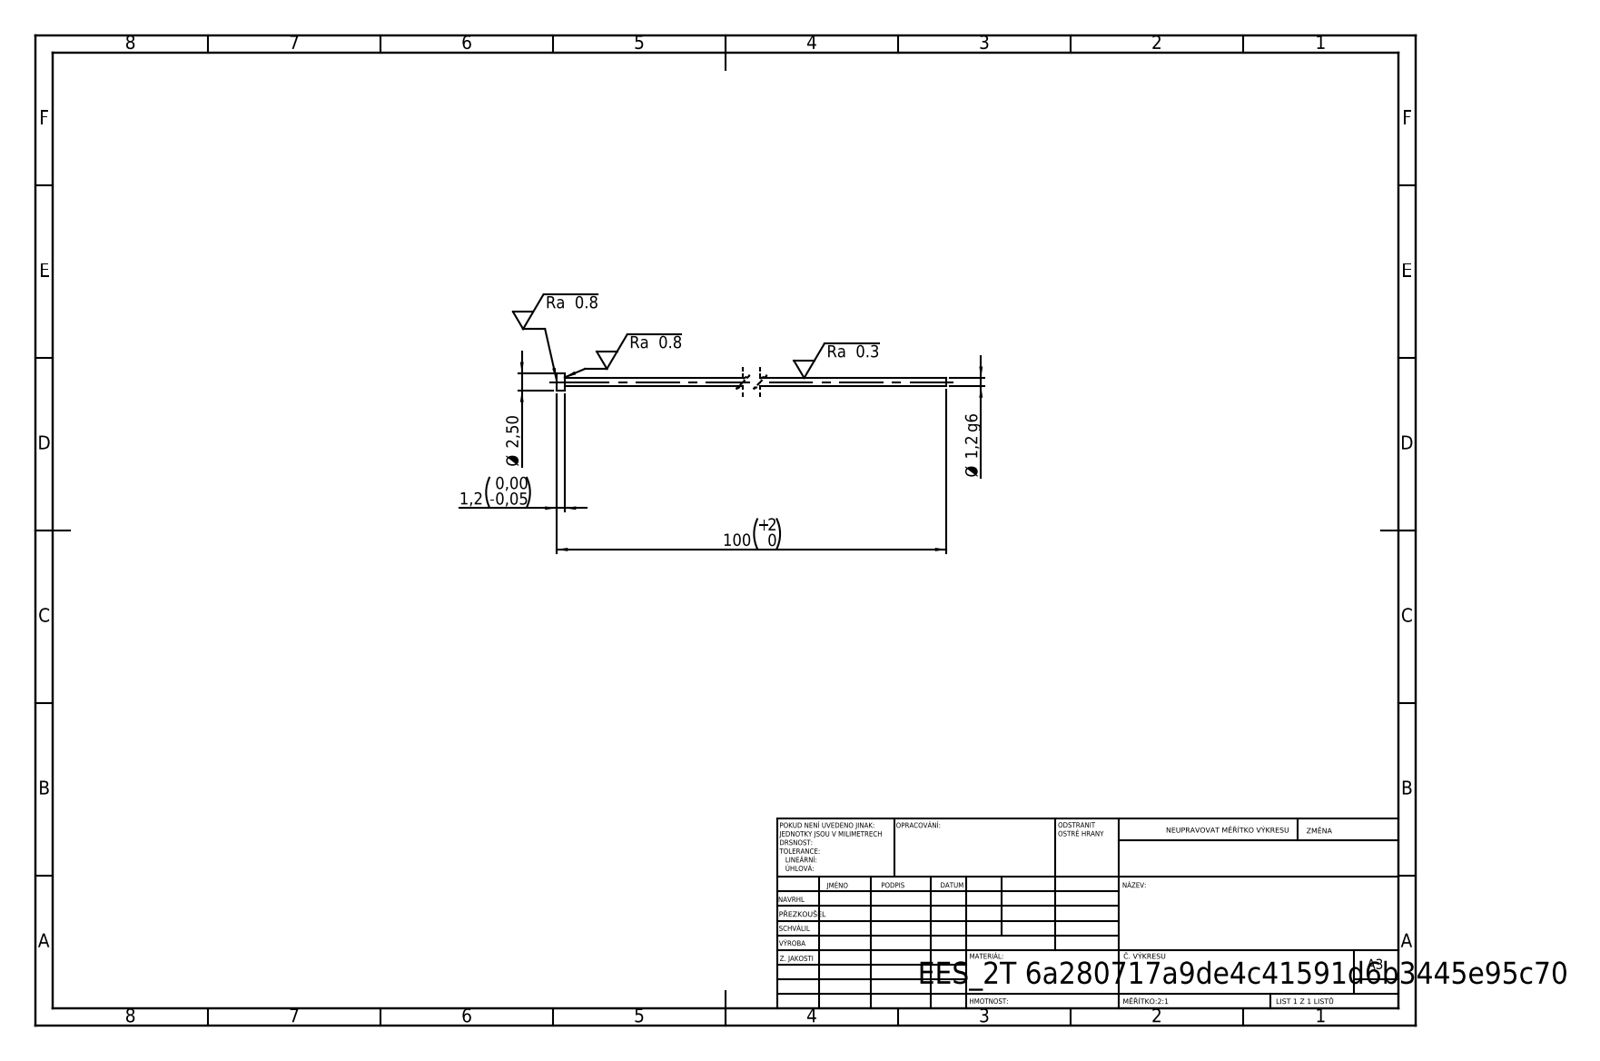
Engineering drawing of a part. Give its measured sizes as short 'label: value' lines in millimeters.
written by: SolidWorks 2019 (CONFIG_CONTROL_DESIGN)
unit: mm
bodies: 1 solid, 7 faces (3 planar, 4 cylindrical, 0 other)
size: 99.8 × 2.5 × 2.5
volume: 117 mm³; area: 391 mm²
bosses: 1× ⌀2.5, 1× ⌀1.2
face distances: 1.2, 99.8, 98.6
